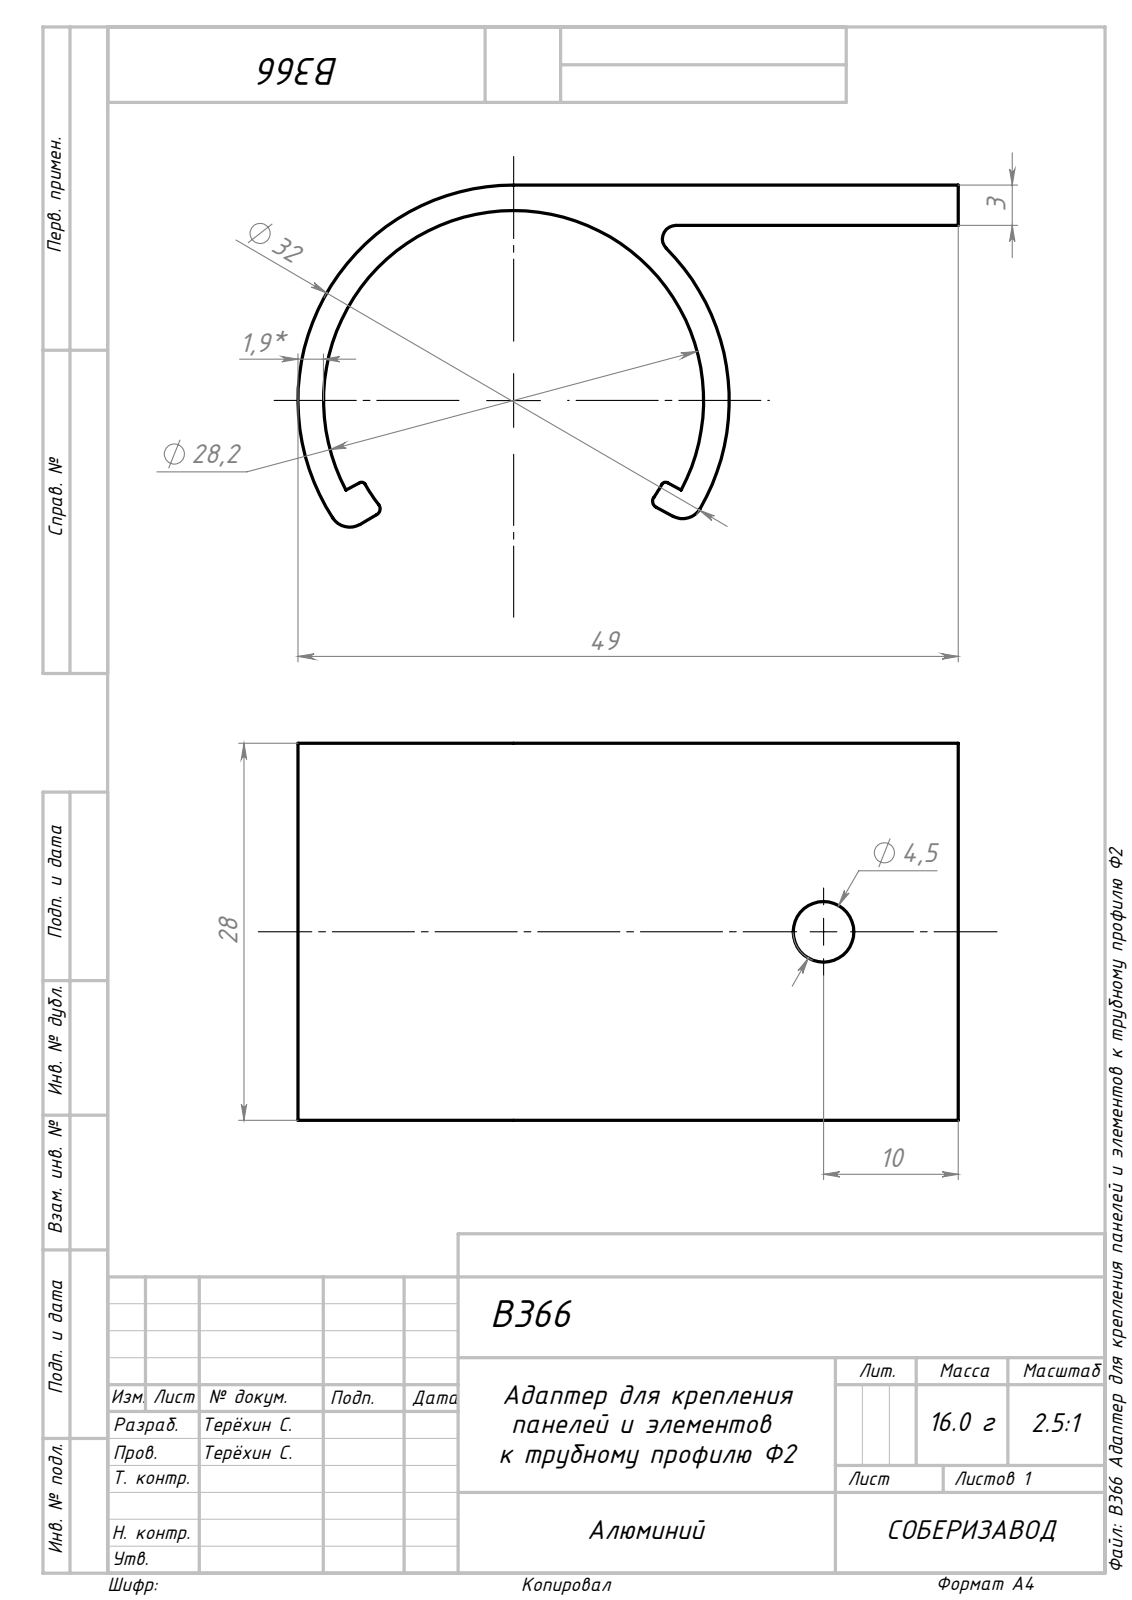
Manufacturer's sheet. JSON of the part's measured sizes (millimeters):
{"part_name": "B366 Адаптер для крепления панелей и элементов к трубному профилю Ф2", "step_written_by": "SolidWorks 2022 (AUTOMOTIVE_DESIGN)", "units": "millimeters", "bodies": {"solids": 1, "faces": 29, "planar": 9, "cylindrical": 17, "other": 3}, "overall_size": [49, 28, 25.41], "volume_mm3": 5930, "surface_area_mm2": 5697, "round_holes": [[4.5, 1]], "partial_cylinders_radius": [[0.3, 2], [0.5, 2], [1.5, 2], [1, 1], [12.65, 1], [14.1, 1], [16, 1]], "face_to_face_distances": [3, 28, 1.99]}
